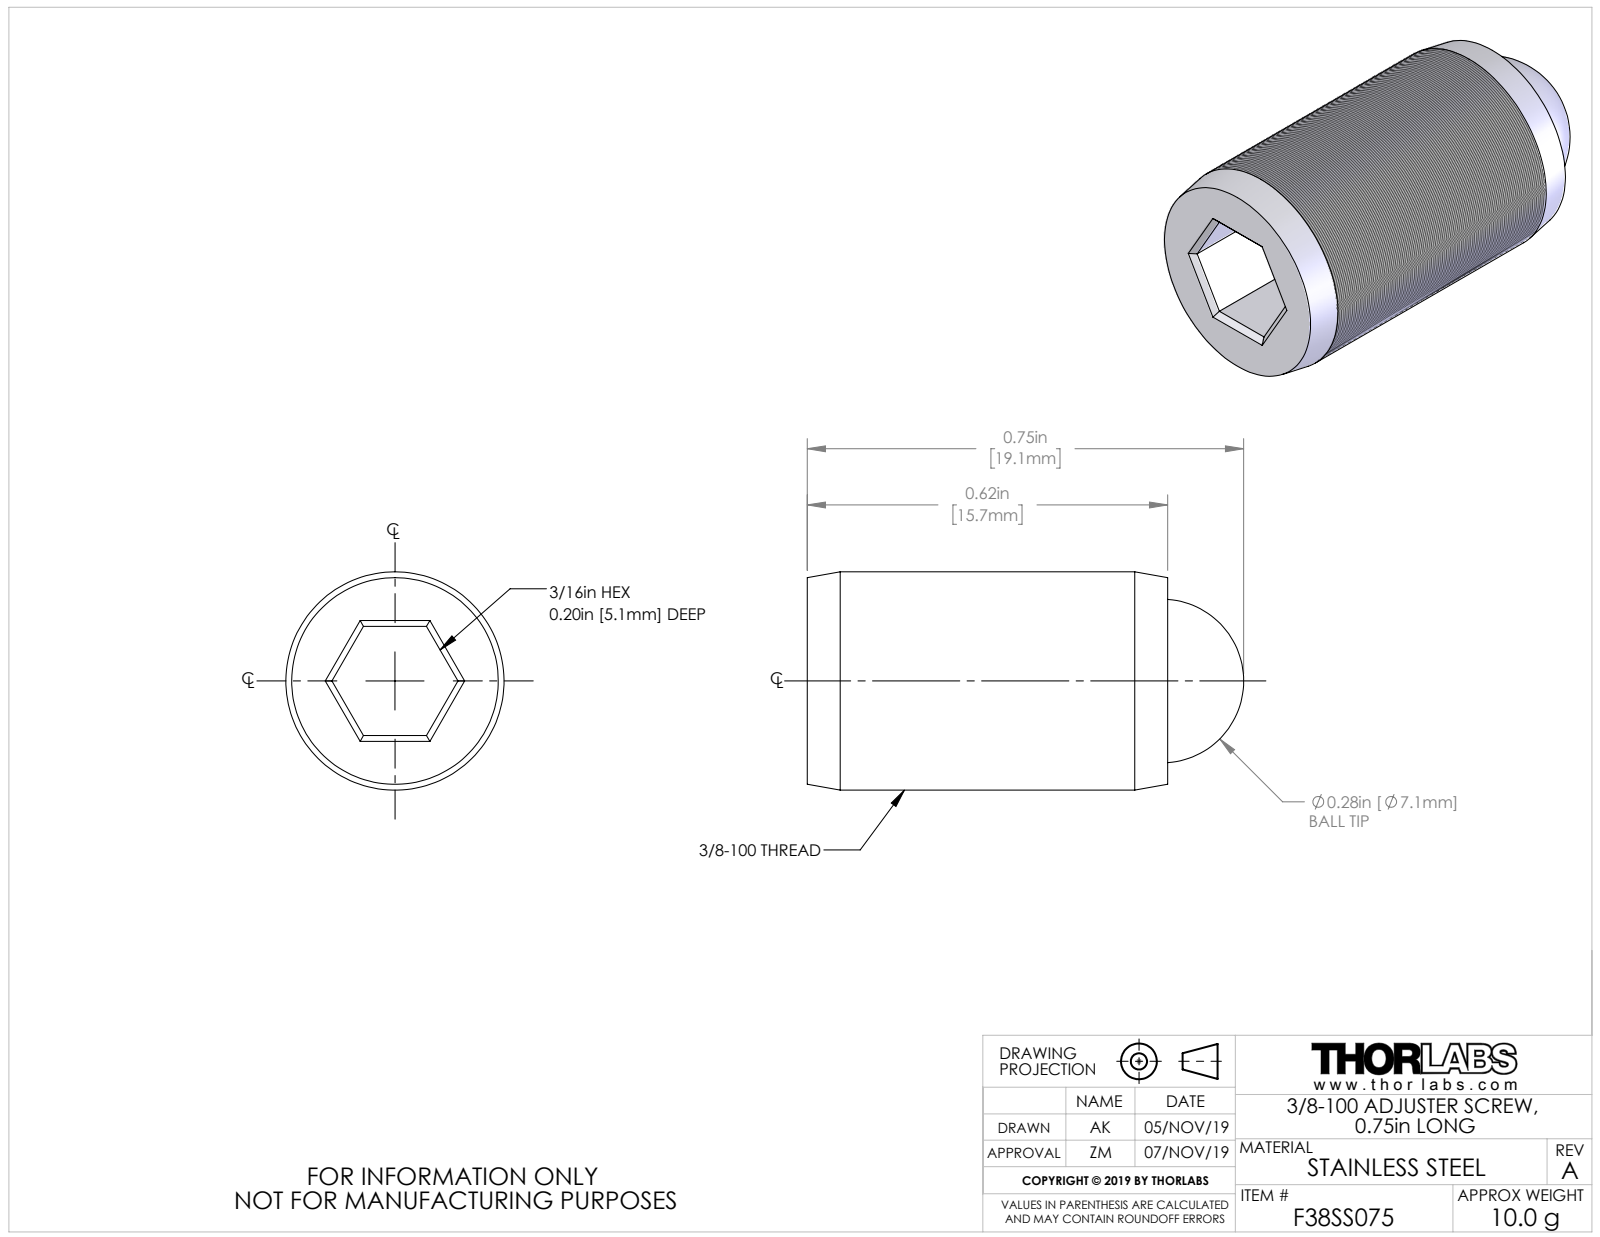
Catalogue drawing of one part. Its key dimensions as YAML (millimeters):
part_name: "TTN200013-E0W"
step_written_by: "SolidWorks 2018 (AUTOMOTIVE_DESIGN)"
units: millimeters
bodies: {solids: 2, faces: 27, planar: 15, cylindrical: 4, other: 8}
overall_size: [19.1, 9.5, 9.5]
volume: 1100
surface_area: 895
round_holes:
  - {diameter: 7.2, count: 1}
round_bosses_or_shafts:
  - {diameter: 9.5, count: 1}
face_to_face_distances: [4.7, 15.7, 5.1, 10.6]
